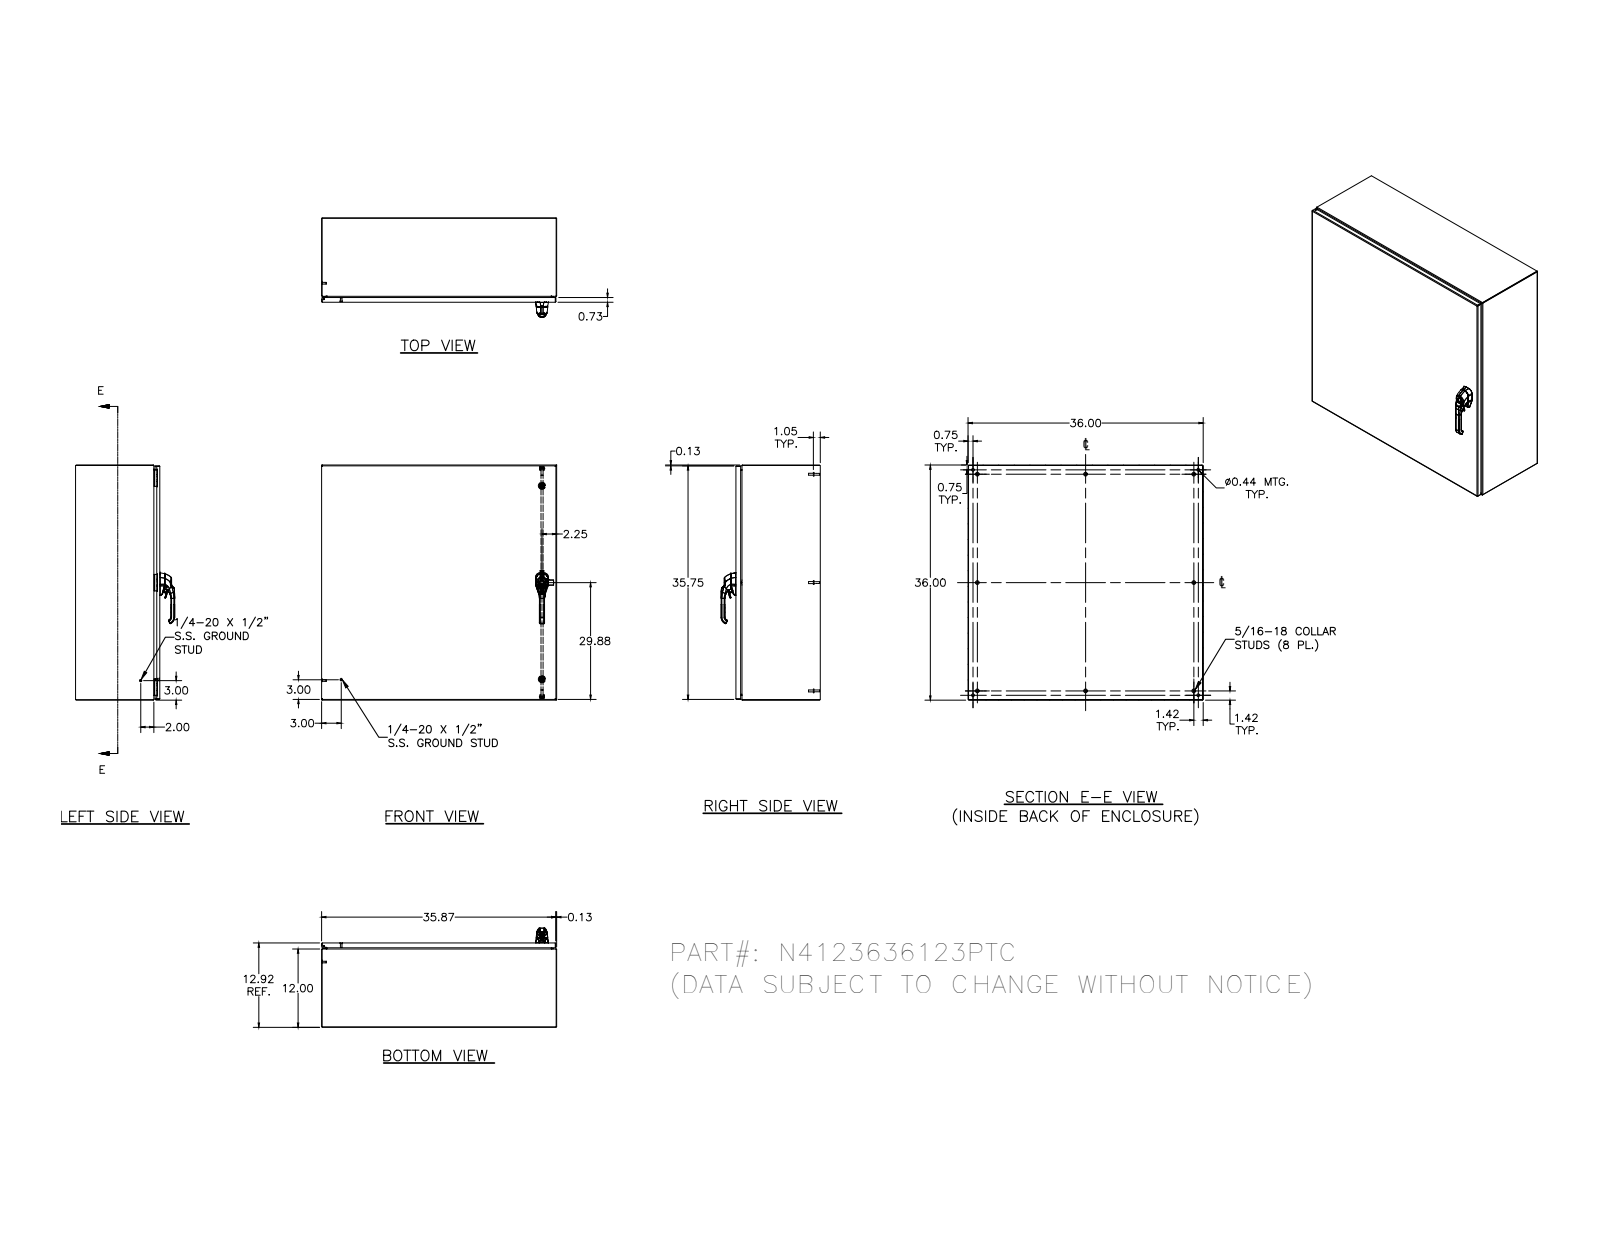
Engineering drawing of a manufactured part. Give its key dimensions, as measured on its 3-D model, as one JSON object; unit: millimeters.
{"part_name": "N4123636123PTC; N4123636123PTCBLR; N41236123PTCTB; HFW328176 (+8 more)", "step_written_by": "Autodesk Inventor 2011 (AUTOMOTIVE_DESIGN)", "units": "millimeters", "bodies": {"solids": 64, "faces": 3420, "planar": 1104, "cylindrical": 1269, "other": 1047}, "overall_size": [914.4, 914.4, 385.7], "volume_mm3": 5649000, "surface_area_mm2": 6068000, "round_holes": [[4.8, 7], [2.4, 6], [3.9, 6], [4.2, 6], [4.4, 6], [4.2, 4], [5, 4], [11.1, 4], [4, 3], [5.4, 3], [6, 3], [9, 3]], "round_bosses_or_shafts": [[6.4, 14], [14.3, 8], [7.6, 8], [7, 8], [9.1, 6], [8.1, 6], [6.5, 6], [4.2, 6]], "partial_cylinders_radius": [[0.5, 174], [0.3, 83], [1.3, 38], [0.8, 32], [3, 28], [0.4, 26], [3.2, 21], [0.5, 19]], "face_to_face_distances": [1.9, 326.2, 912.5, 324.3, 328.1, 910.6, 914.4, 23.3, 302.9, 18.8], "hole_center_spacings": [406.4, 406.6, 812.8, 0.4, 16.8, 389.6, 406.2, 423.2]}
